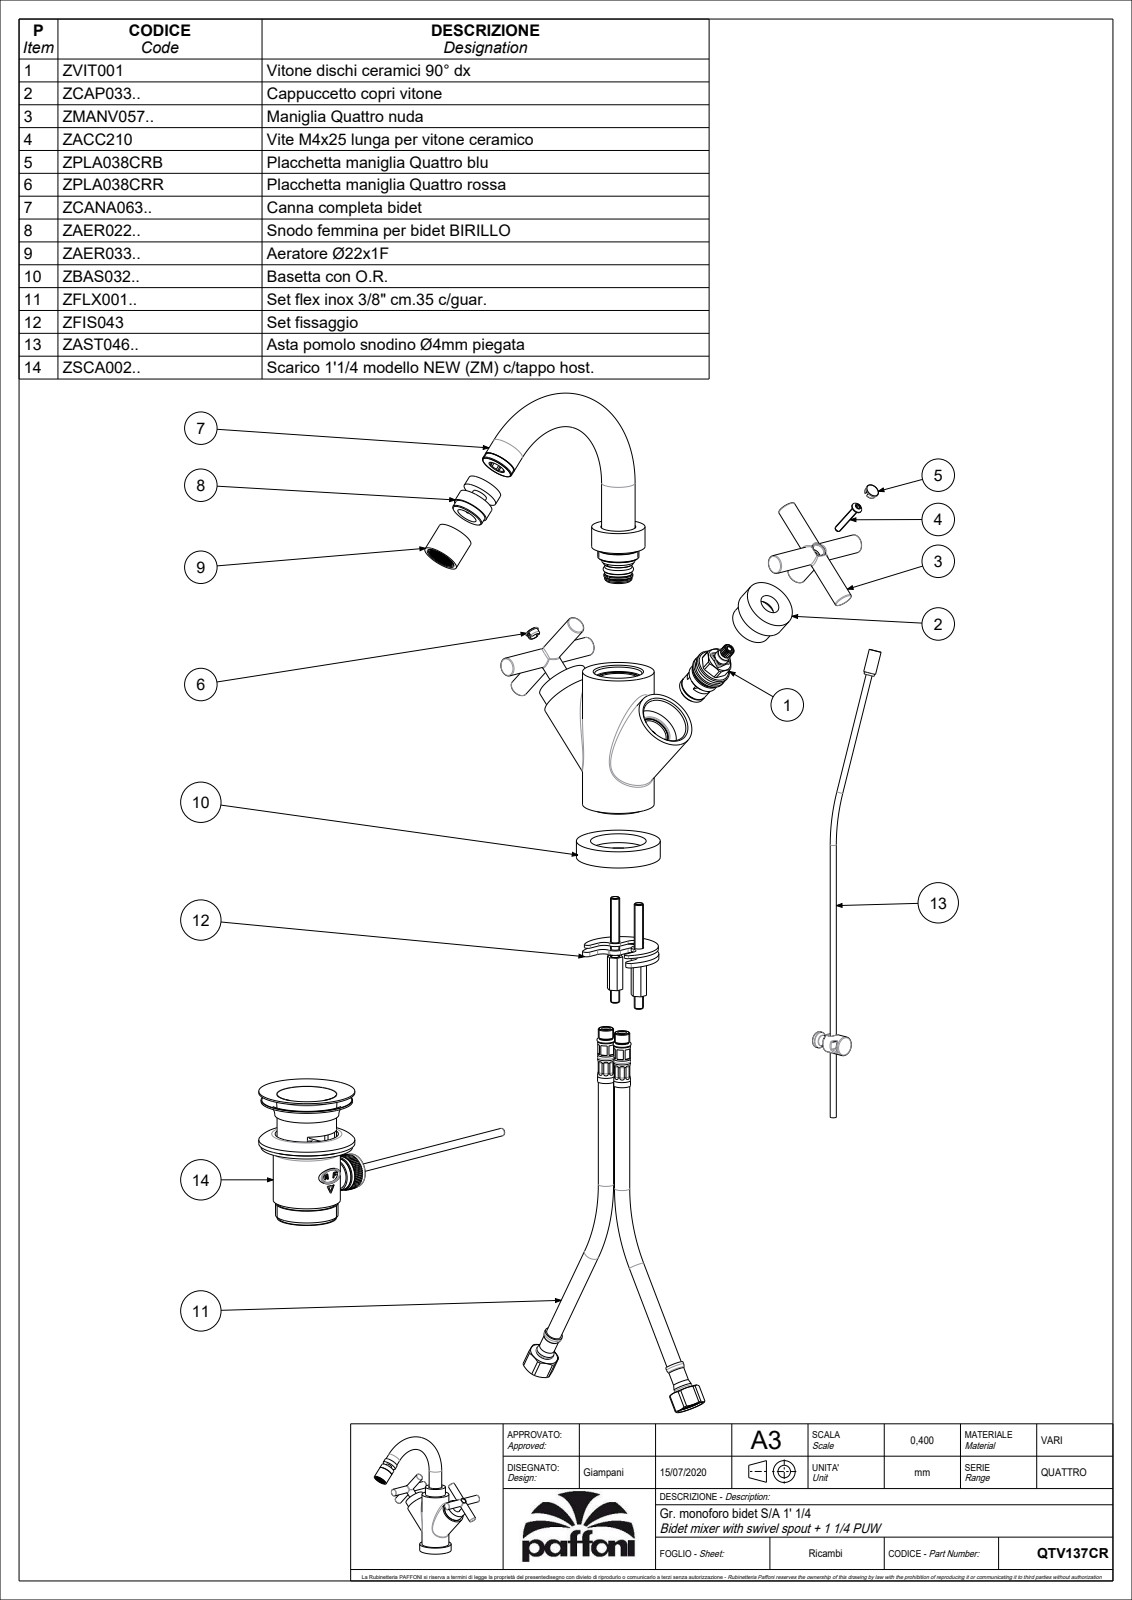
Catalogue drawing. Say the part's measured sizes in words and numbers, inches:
The part is named "QTV137CR". Its 3-D file was written by "CREO PARAMETRIC BY PTC INC, 2020044 (CONFIG_CONTROL_DESIGN)". It is 7 solids with 2449 faces: 1893 planar, 316 cylindrical and 240 other. Overall it measures 8.472 by 7.583 by 7.208 inches. Its volume is 18.64 cubic inches and its surface area 175 square inches. Round holes: 5 of diameter 0.276, 4 of diameter 0.354, 4 of diameter 0.748, 3 of diameter 0.315, 2 of diameter 0.13, 2 of diameter 0.177, 2 of diameter 0.181, 2 of diameter 0.346, 2 of diameter 0.374, 2 of diameter 0.406, 2 of diameter 0.433, 2 of diameter 0.531. Round bosses or shafts: 4 of diameter 0.472, 3 of diameter 0.945, 2 of diameter 1.575, 2 of diameter 1.339, 2 of diameter 1.102, 2 of diameter 0.866, 2 of diameter 0.843, 2 of diameter 0.732. Partial cylindrical surfaces (rounded edges, fillets, slot ends): 34 of radius 0.004, 4 of radius 0.02, 4 of radius 0.039, 2 of radius 0.118, 2 of radius 0.366, 2 of radius 0.37. The main face-to-face distances are 0.472, 0.197, 0.157, 0.039, 0.531, 0.433, 0.236, 0.354, 0.059, 3.976. The hole center spacings are 0.335, 0.625, 0.394, 0.591.
